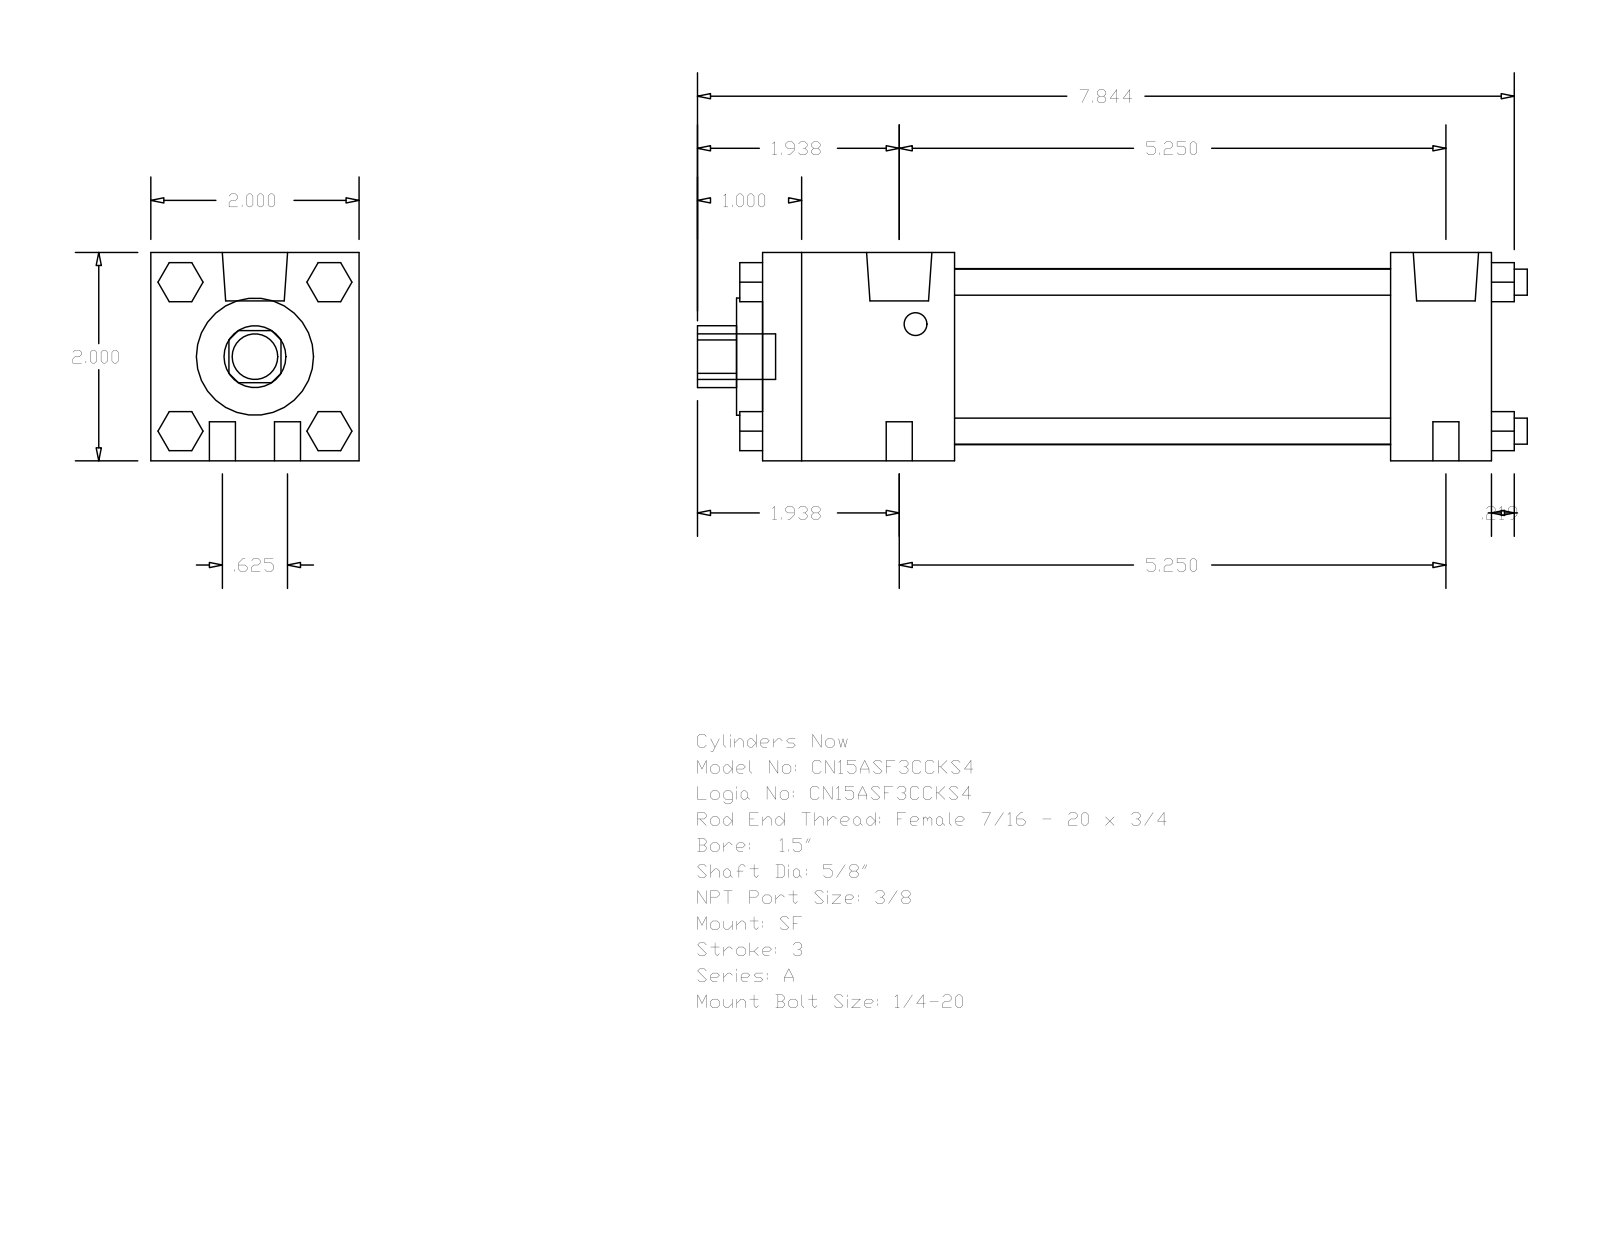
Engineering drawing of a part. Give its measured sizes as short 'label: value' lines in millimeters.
name: A_SF__0150_0.625
written by: GSSL Pune (CONFIG_CONTROL_DESIGN)
unit: mm
bodies: 0 solids, 124 faces (94 planar, 30 cylindrical, 0 other)
size: 202.41 × 50.8 × 50.8
holes: 1× ⌀15.88, 1× ⌀28.57, 1× ⌀42.93
bosses: 8× ⌀6.35, 2× ⌀15.93, 2× ⌀5.56, 1× ⌀11.11
rounds: 1× R7.54
face distances: 50.8, 177.8, 46.83, 153.19, 106.36, 130.97, 24.61, 9.52, 6.35, 53.18
